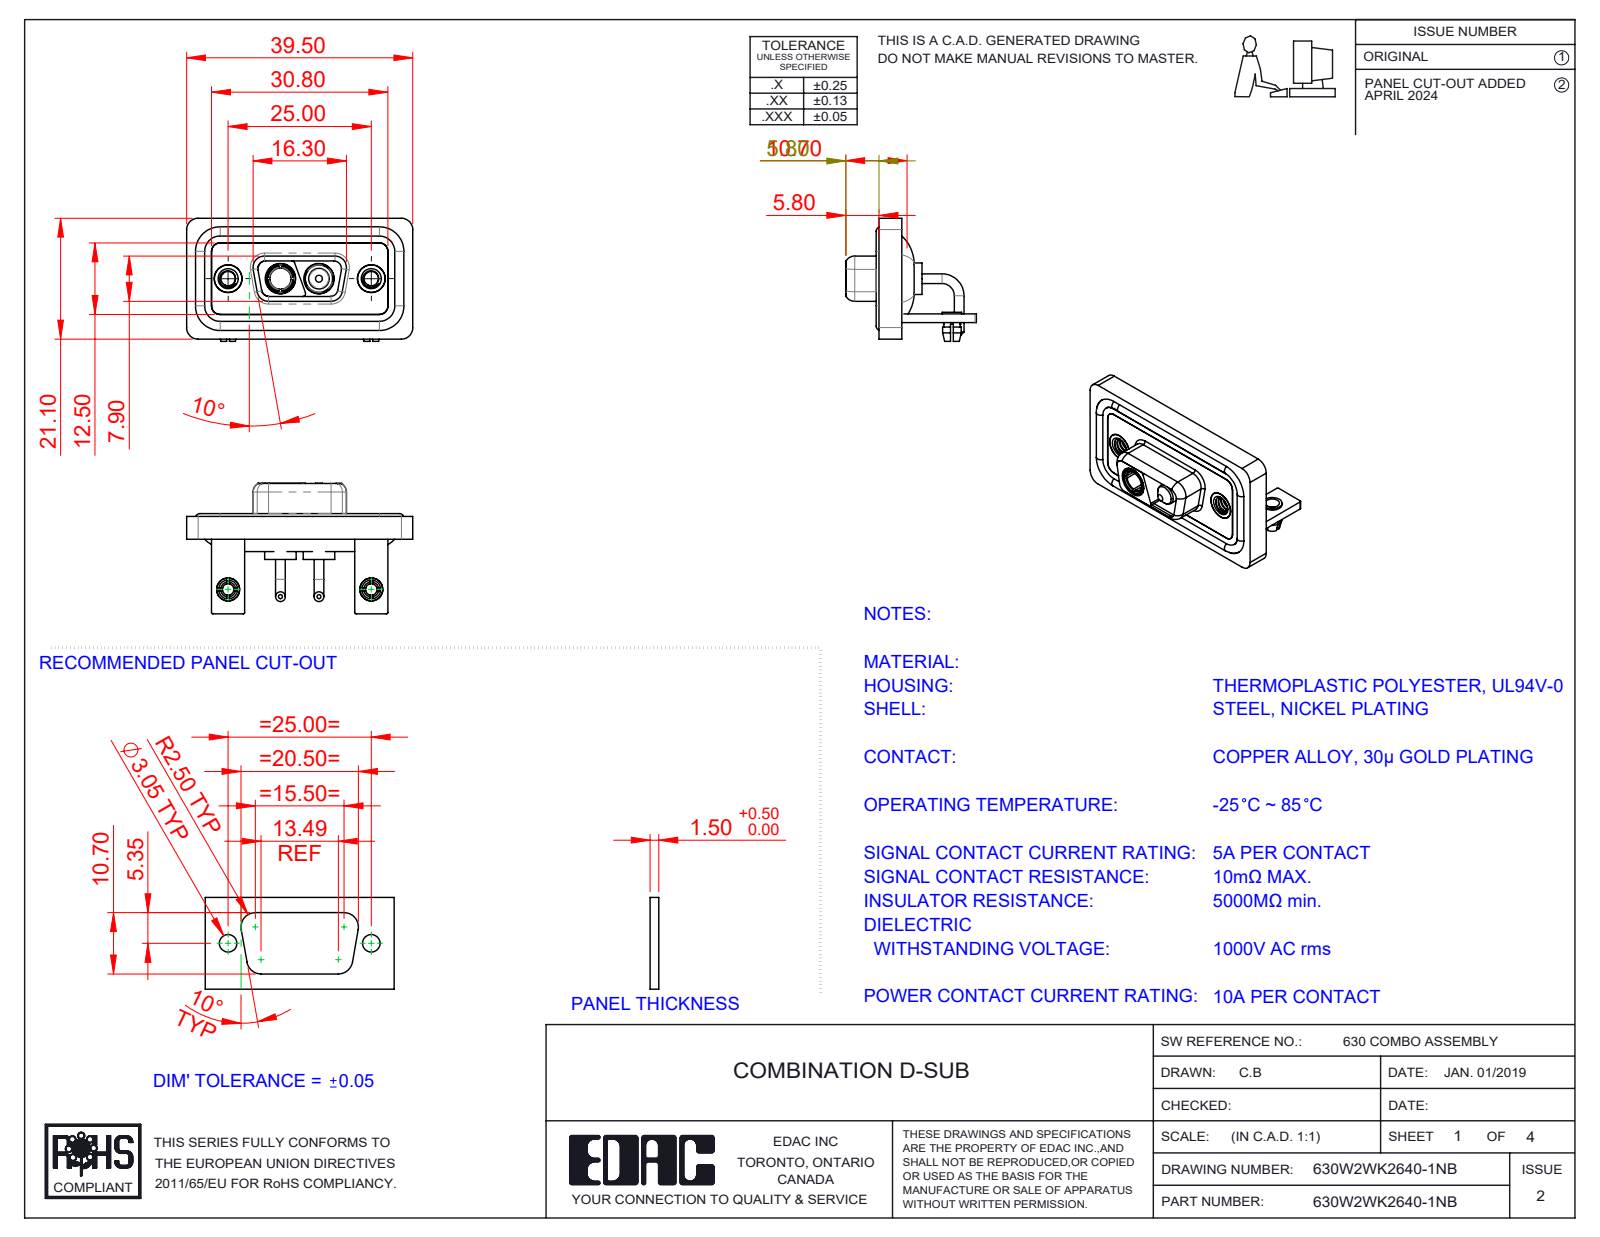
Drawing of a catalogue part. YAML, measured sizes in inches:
part_name: "Power Socket_10A RA; 630Combo Board Lock_50 Contacts; 630Combo Waterproof Housing_09 Contacts; 630Combo Threaded Rivet_A (+6 more)"
step_written_by: "SolidWorks 2023 (CONFIG_CONTROL_DESIGN)"
units: inches
bodies: {solids: 15, faces: 642, planar: 212, cylindrical: 289, other: 141}
overall_size: [1.555, 0.898, 0.846]
volume: 0.304
surface_area: 12.93
round_holes:
  - {diameter: 0.098, count: 4}
  - {diameter: 0.191, count: 4}
  - {diameter: 0.079, count: 2}
  - {diameter: 0.126, count: 2}
  - {diameter: 0.157, count: 2}
  - {diameter: 0.159, count: 2}
  - {diameter: 0.197, count: 2}
  - {diameter: 0.209, count: 2}
  - {diameter: 0.146, count: 1}
round_bosses_or_shafts:
  - {diameter: 0.067, count: 4}
  - {diameter: 0.063, count: 4}
  - {diameter: 0.217, count: 2}
  - {diameter: 0.205, count: 2}
  - {diameter: 0.195, count: 2}
  - {diameter: 0.189, count: 2}
  - {diameter: 0.187, count: 2}
  - {diameter: 0.157, count: 2}
partial_cylinders:
  - {radius: 0.079, count: 19}
  - {radius: 0.059, count: 18}
  - {radius: 0.01, count: 16}
  - {radius: 0.053, count: 8}
  - {radius: 0.063, count: 8}
  - {radius: 0.02, count: 7}
  - {radius: 0.024, count: 4}
  - {radius: 0.026, count: 4}
face_to_face_distances: [0.016, 0.114, 0.059, 0.043, 0.146, 0.071, 0.031, 0.098, 0.063, 0.122]
hole_center_spacings: [0.36, 0.624, 0.984, 0.265]
